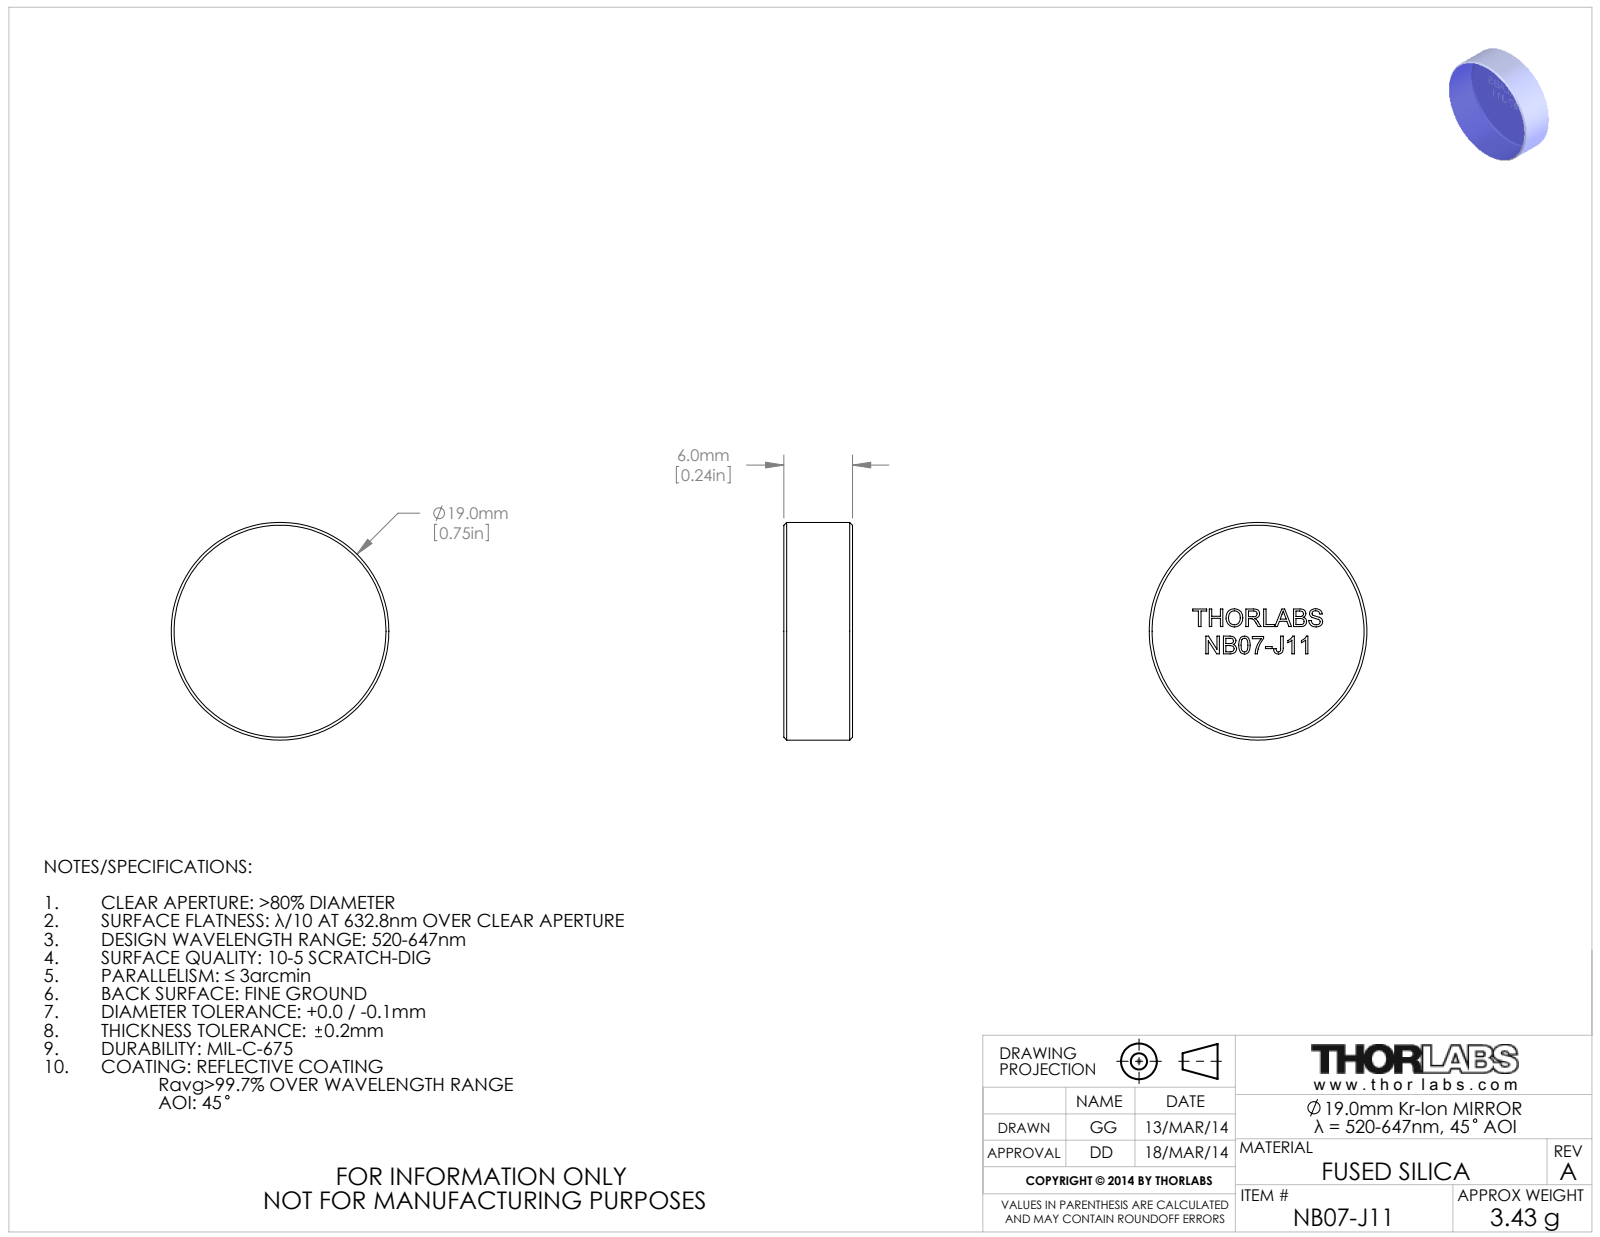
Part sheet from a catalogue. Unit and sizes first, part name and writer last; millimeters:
Units: millimetres
Overall size (bounding box): 19 × 19 × 6
Round bosses / shafts (diameter × count): ⌀19 ×1
Main face-to-face distances: 6, 1.5, 1.9, 1.2, 2.4, 2.4, 4.1, 1, 0.3, 2.2
Volume: 1 700 mm³ · Surface area: 908 mm²
Bodies: 1 solid, 206 faces (127 planar, 2 cylindrical, 77 other)
Part name (STEP PRODUCT): TTN024119-E0W
STEP written by: SolidWorks 2012 (CONFIG_CONTROL_DESIGN)
